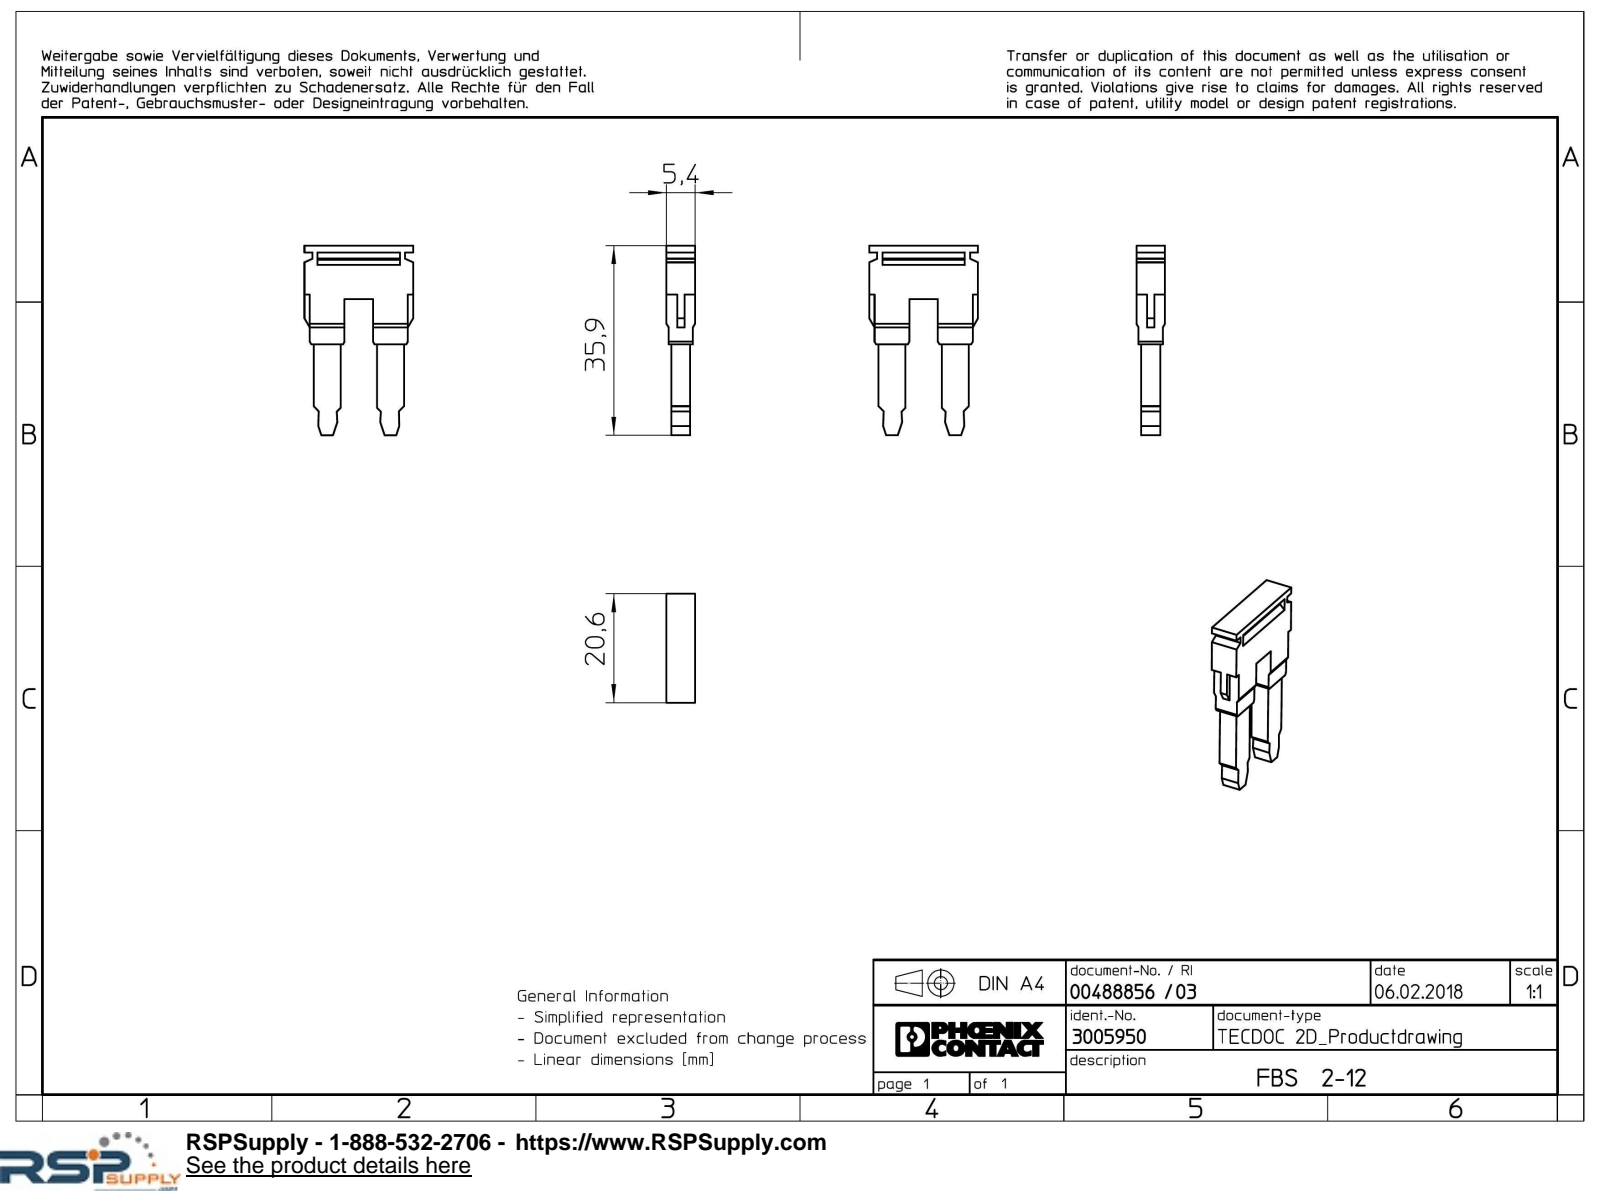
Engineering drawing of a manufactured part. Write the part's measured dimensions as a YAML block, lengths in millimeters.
part_name: "FBS_2_12-select"
step_written_by: "Creo Elements/Direct Modeling 20.1A 29-Sep-2018 (C) Parametric Technology GmbH (AUTOMOTIVE_DESIGN)"
units: millimeters
bodies: {solids: 1, faces: 76, planar: 76, cylindrical: 0, other: 0}
overall_size: [35.9, 20.6, 5.4]
volume: 2147
surface_area: 1832
face_to_face_distances: [0.9, 4.5, 5.4, 0.75, 12, 3.6, 5.85, 5.1, 0.5, 11.25]
